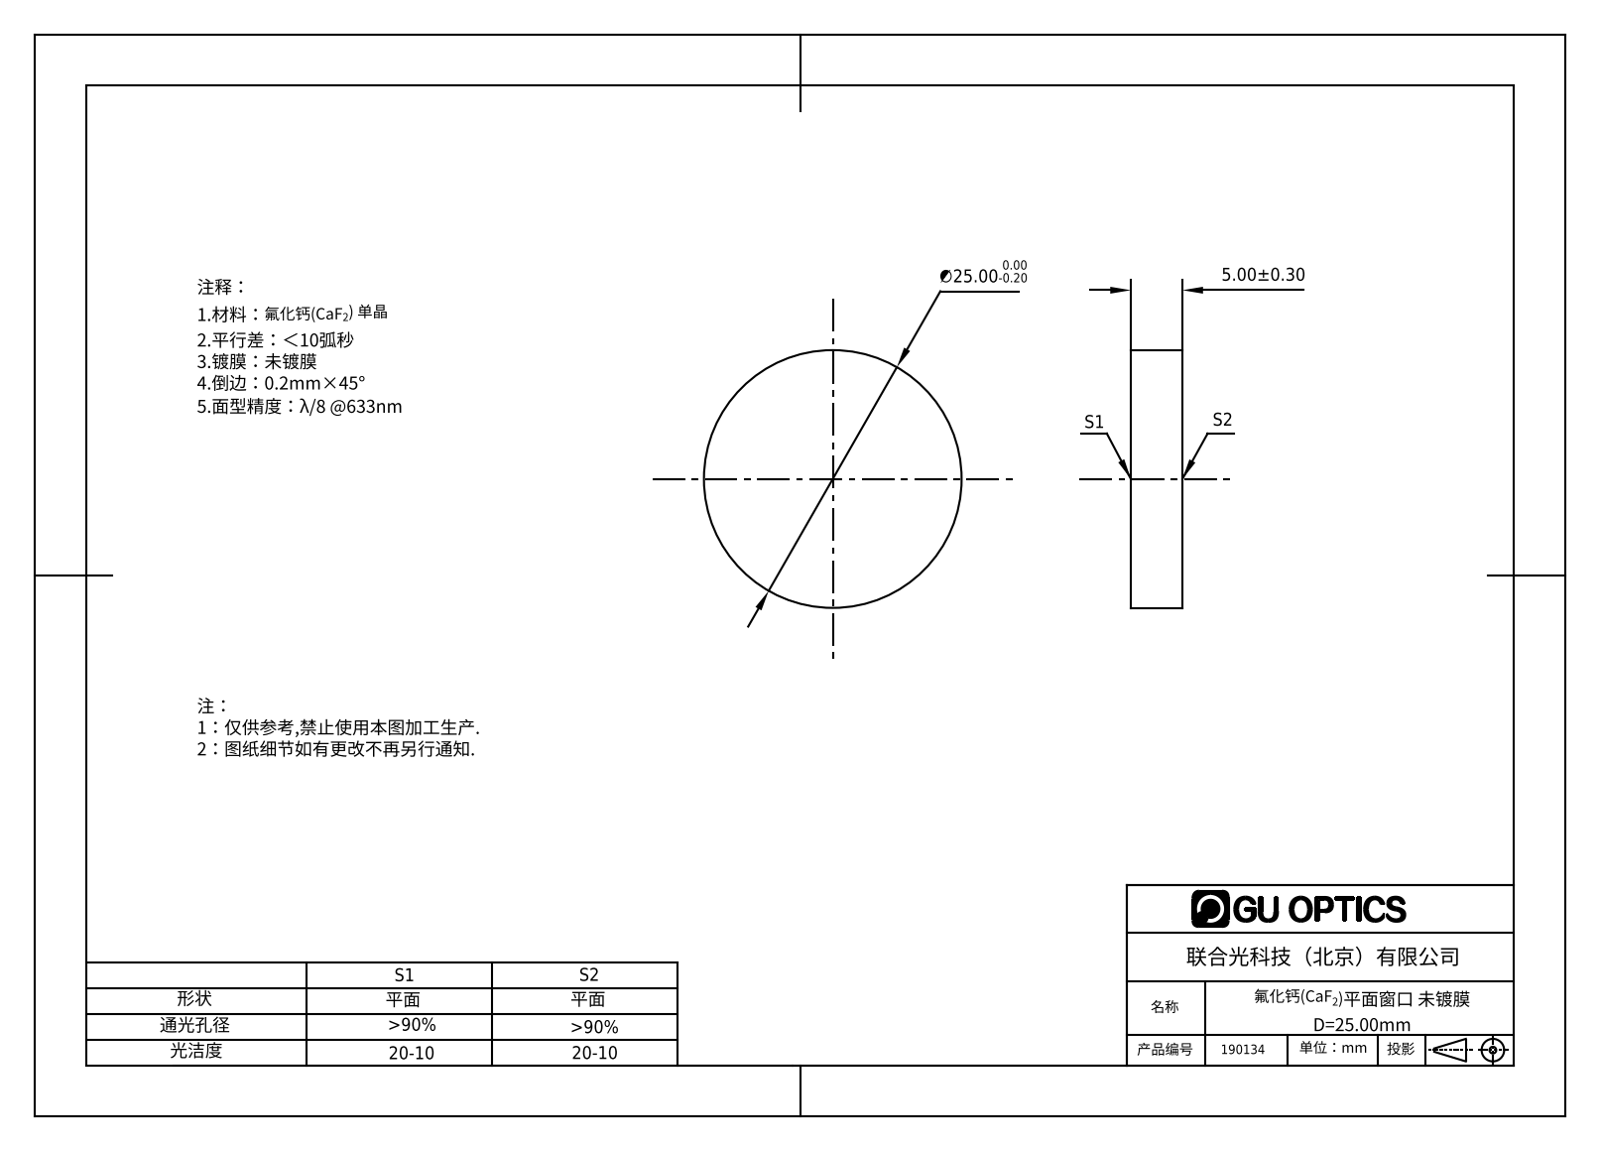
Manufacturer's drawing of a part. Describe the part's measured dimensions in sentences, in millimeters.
The part is named "190134". Its 3-D file was written by "SolidWorks 2016 (AUTOMOTIVE_DESIGN)". It is 1 solid with 4 faces: 2 planar, 2 cylindrical and 0 other. Overall it measures 25 by 25 by 5 millimeters. Its volume is 2 454 cubic millimeters and its surface area 1 374 square millimeters. Round bosses or shafts: 1 of diameter 25. The main face-to-face distances are 5.
